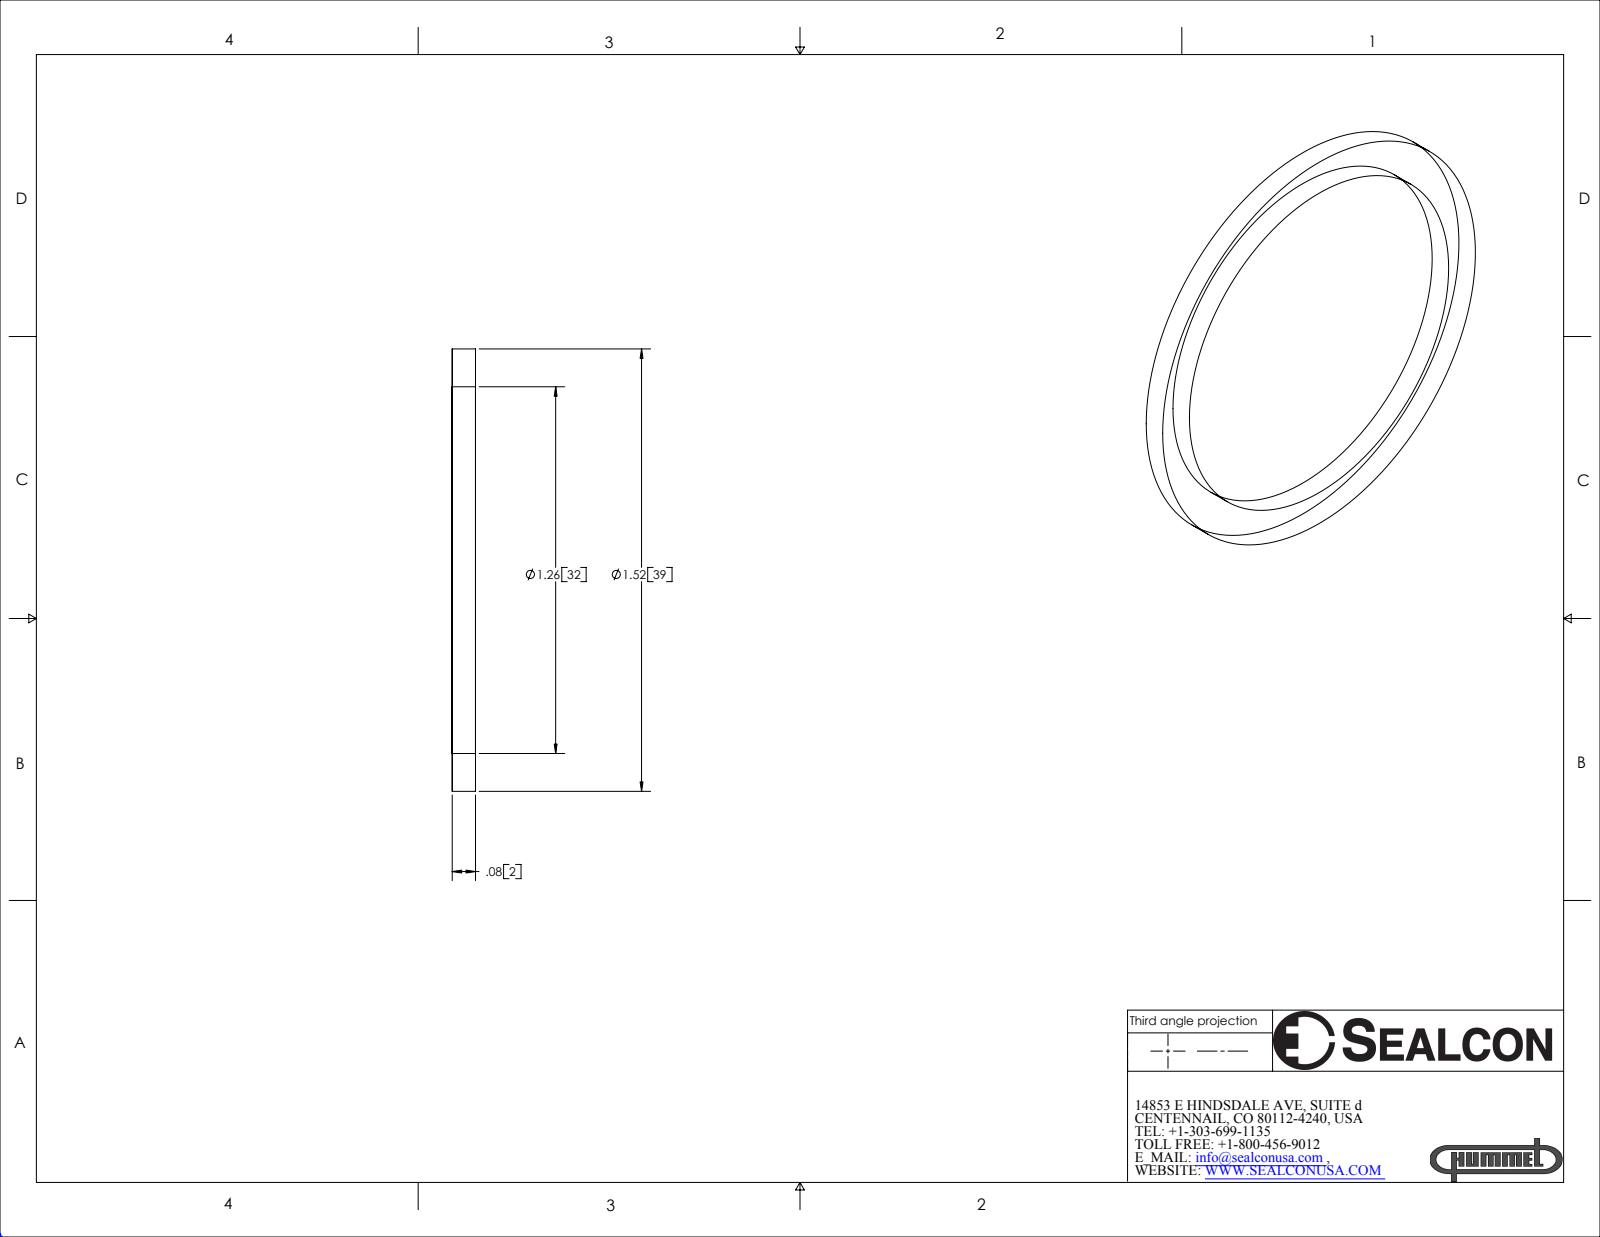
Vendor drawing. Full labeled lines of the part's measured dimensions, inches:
Part name (STEP PRODUCT): MS-32-NY
STEP written by: SolidWorks 2007 (CONFIG_CONTROL_DESIGN)
Units: inches
Bodies: 1 solid, 6 faces (2 planar, 4 cylindrical, 0 other)
Overall size (bounding box): 1.52 × 1.52 × 0.08
Volume: 0.045 in³ · Surface area: 1.834 in²
Round holes (diameter × count): ⌀1.26 ×1
Round bosses / shafts (diameter × count): ⌀1.52 ×1
Main face-to-face distances: 0.08
